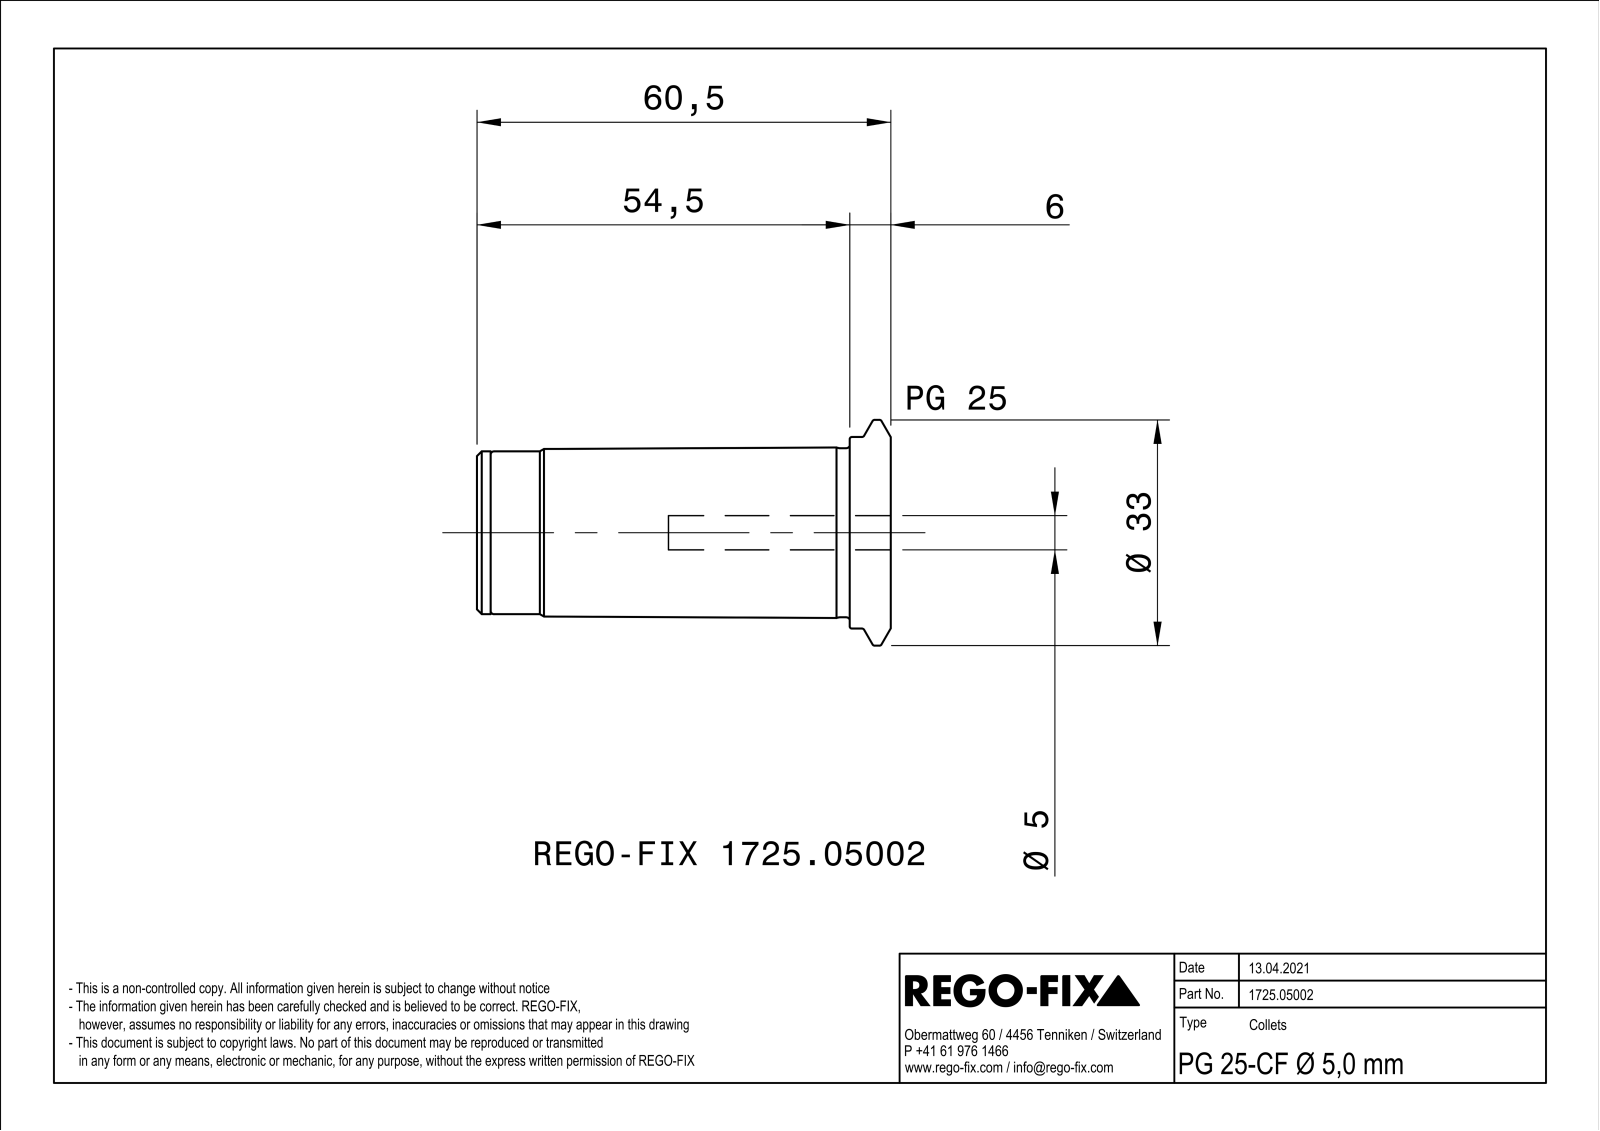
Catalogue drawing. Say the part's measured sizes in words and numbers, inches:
The part is named "NOCUT". Its 3-D file was written by "SIEMENS PLM Software Solid Edge ST10 (AUTOMOTIVE_DESIGN)". It is 1 solid with 91 faces: 23 planar, 28 cylindrical and 40 other. Overall it measures 2.382 by 1.299 by 1.299 inches. Its volume is 1.579 cubic inches and its surface area 17.21 square inches. Round holes: 3 of diameter 0.098, 1 of diameter 0.205, 1 of diameter 0.272, 1 of diameter 0.323, 1 of diameter 0.354, 1 of diameter 0.824, 1 of diameter 0.874. Round bosses or shafts: 1 of diameter 1.299, 1 of diameter 1.102, 1 of diameter 0.972, 1 of diameter 0.937, 1 of diameter 0.803, 1 of diameter 0.472. Partial cylindrical surfaces (rounded edges, fillets, slot ends): 3 of radius 0.03, 1 of radius 0.098. The main face-to-face distances are 0.039, 2.382, 2.071, 0.311, 2.303, 0.232, 0.079, 1.969, 0.102, 0.335. The hole center spacings are 0.305, 0.529, 0.528.
